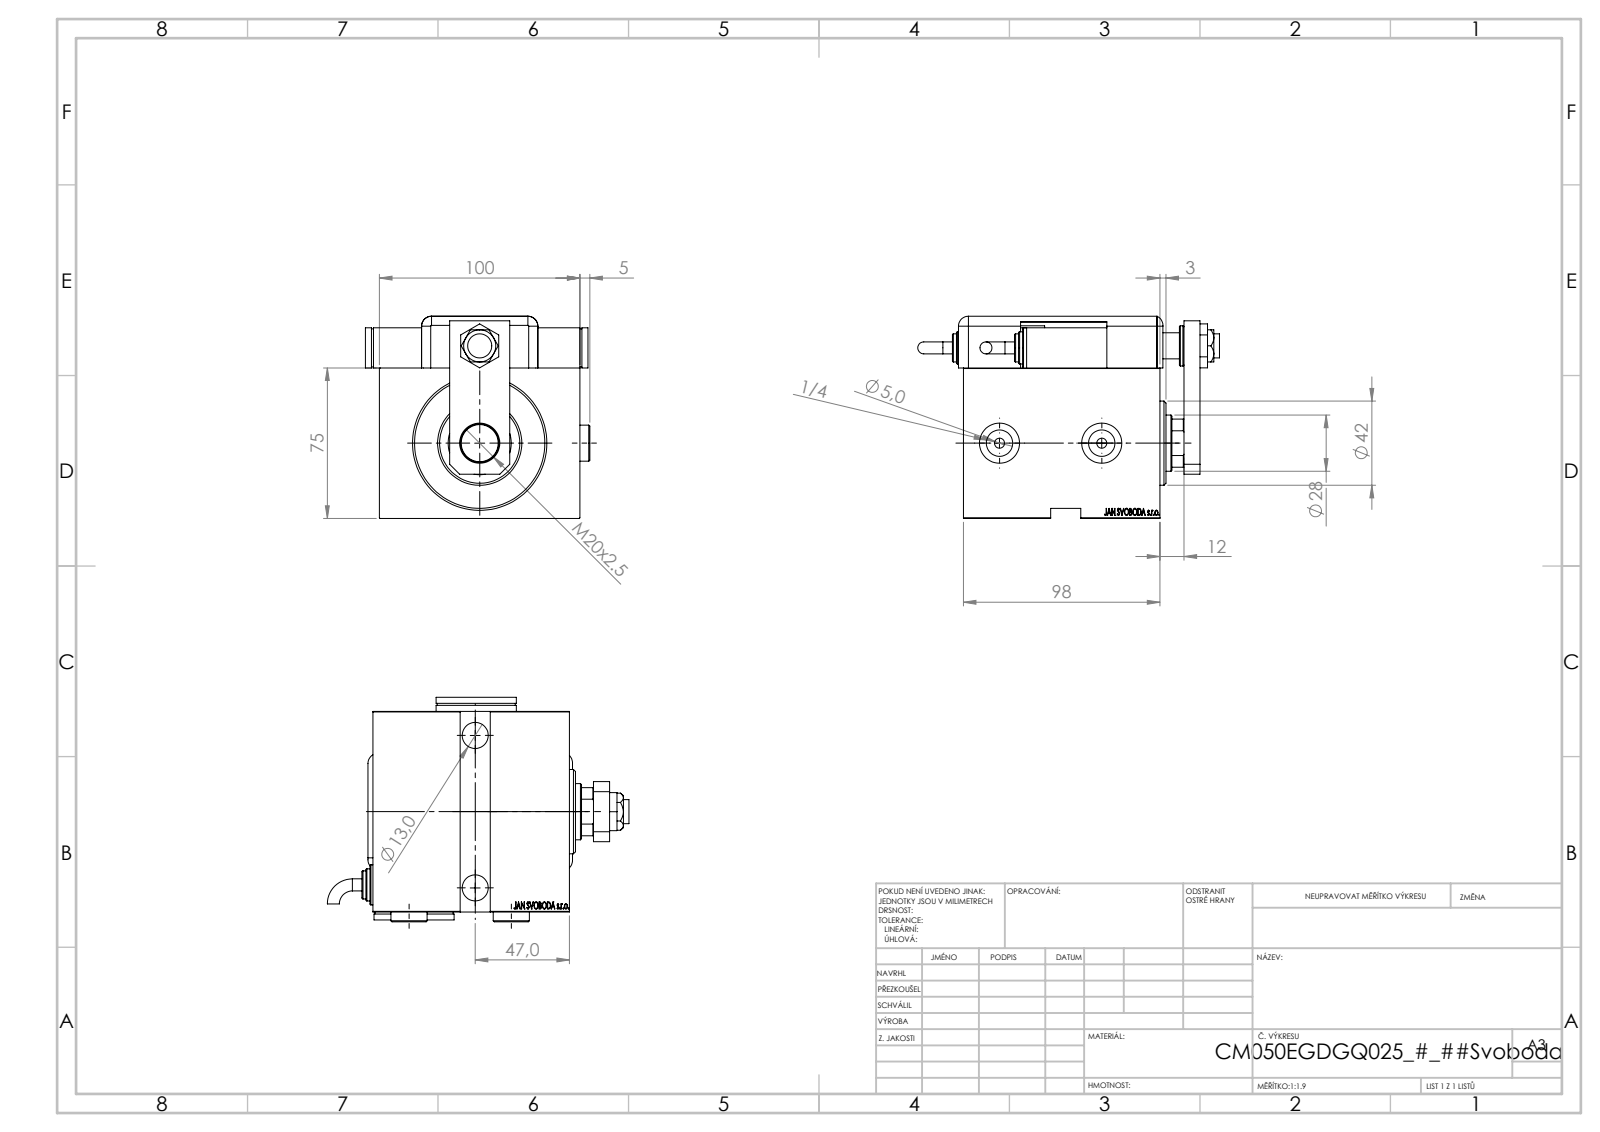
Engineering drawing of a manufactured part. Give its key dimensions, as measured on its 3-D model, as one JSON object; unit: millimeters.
{"part_name": "V450CM_E_Body; ZARAZKA_Q; SWITCH DIM A_G; TYC (+7 more)", "step_written_by": "SolidWorks 2019 (CONFIG_CONTROL_DESIGN)", "units": "millimeters", "bodies": {"solids": 15, "faces": 1286, "planar": 650, "cylindrical": 115, "other": 521}, "overall_size": [150.46, 111.9, 100.8], "volume_mm3": 814074, "surface_area_mm2": 155611, "round_holes": [[13, 3], [20, 3], [4, 2], [5, 2], [8, 2], [13.16, 2], [19, 2], [12, 1], [14, 1], [18.5, 1], [28, 1], [31.5, 1]], "round_bosses_or_shafts": [[20, 3], [18, 2], [16, 2], [14, 2], [6, 2], [52, 1], [42, 1]], "partial_cylinders_radius": [[5, 9], [10, 1], [13.5, 1]], "face_to_face_distances": [3, 75, 98, 100, 14, 20, 84, 79, 100.8, 25.8], "hole_center_spacings": [47.2, 61.22, 20, 48.5, 51, 76]}
